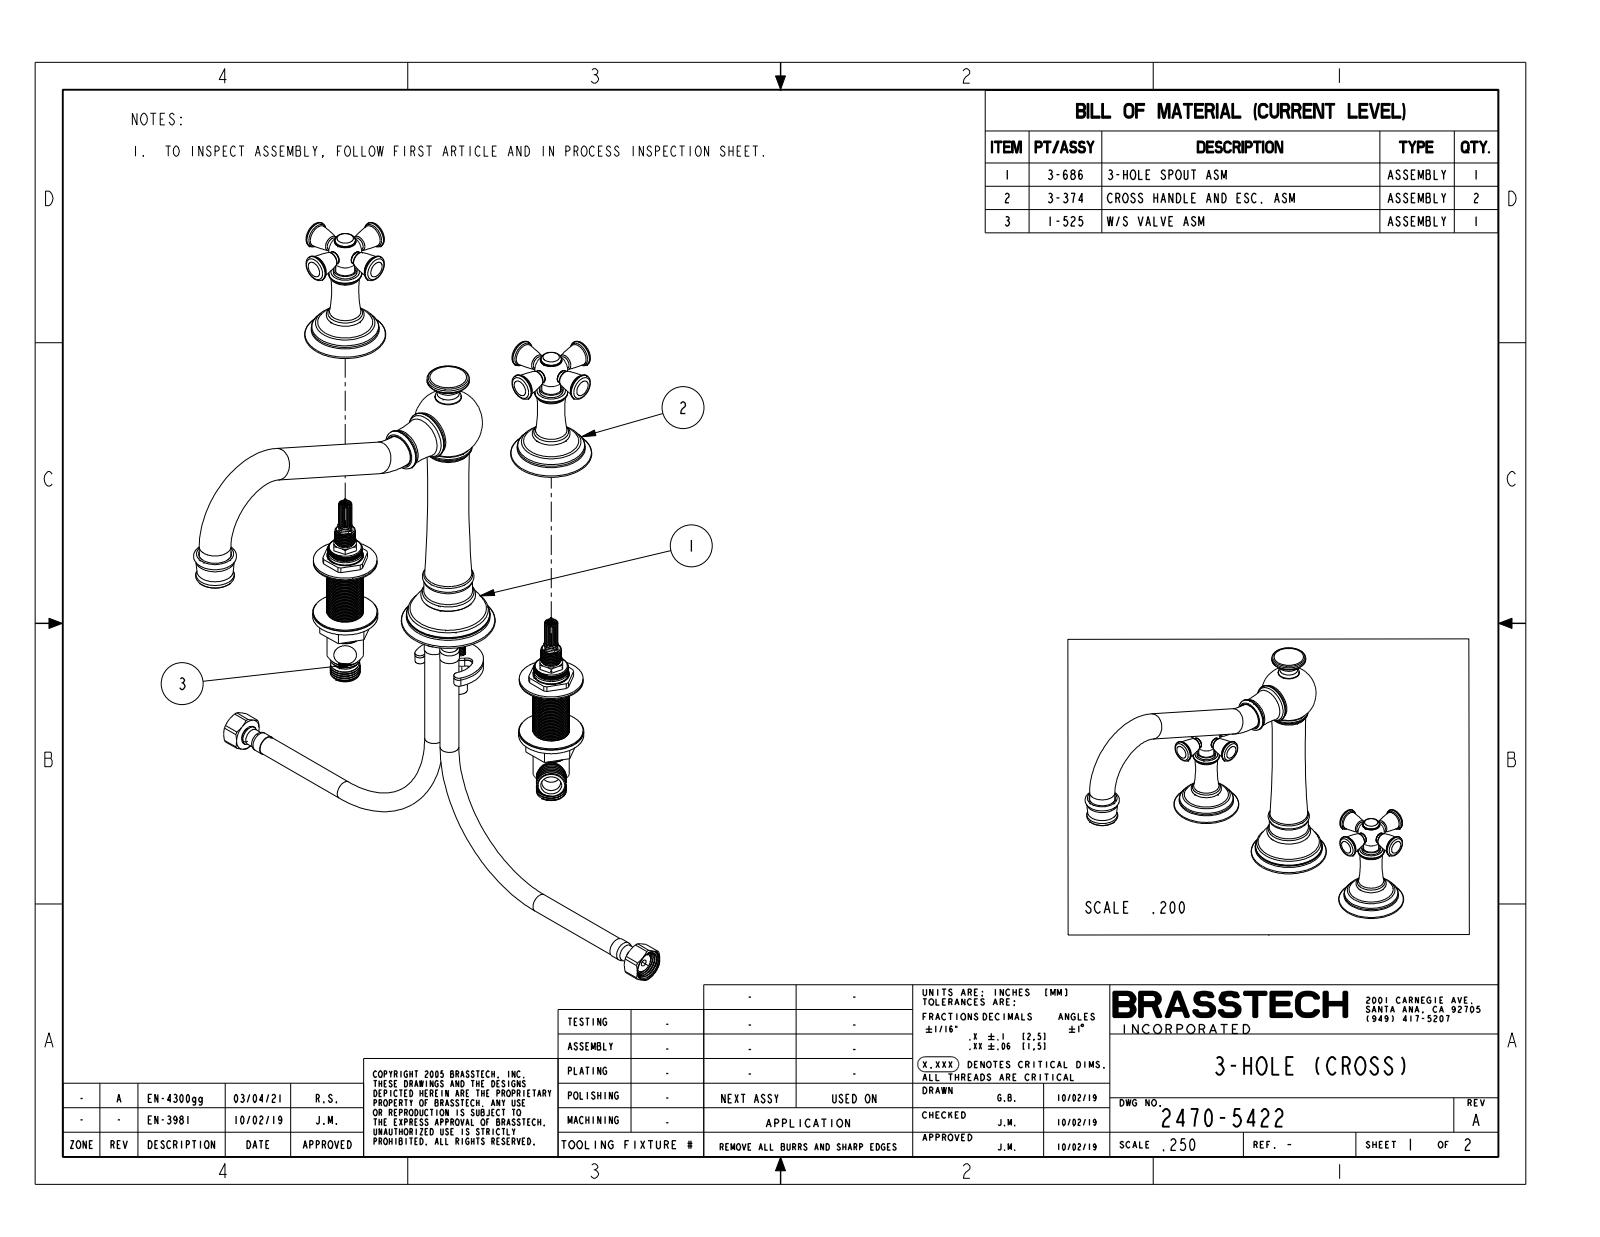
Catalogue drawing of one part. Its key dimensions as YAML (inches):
part_name: "2470-5422"
step_written_by: "CREO PARAMETRIC BY PTC INC, 2018400 (AUTOMOTIVE_DESIGN)"
units: inches
bodies: {solids: 4, faces: 368, planar: 18, cylindrical: 64, other: 286}
overall_size: [10.933, 10.528, 9.211]
volume: 26.71
surface_area: 123.8
round_bosses_or_shafts:
  - {diameter: 0.87, count: 3}
  - {diameter: 0.72, count: 3}
  - {diameter: 0.36, count: 3}
  - {diameter: 0.9, count: 2}
  - {diameter: 0.649, count: 2}
  - {diameter: 0.56, count: 2}
  - {diameter: 0.517, count: 2}
  - {diameter: 1.313, count: 1}
face_to_face_distances: [6.006, 5.984, 0.022, 6, 0.016, 2.14, 3.844, 3.86, 3.866, 2.22]
